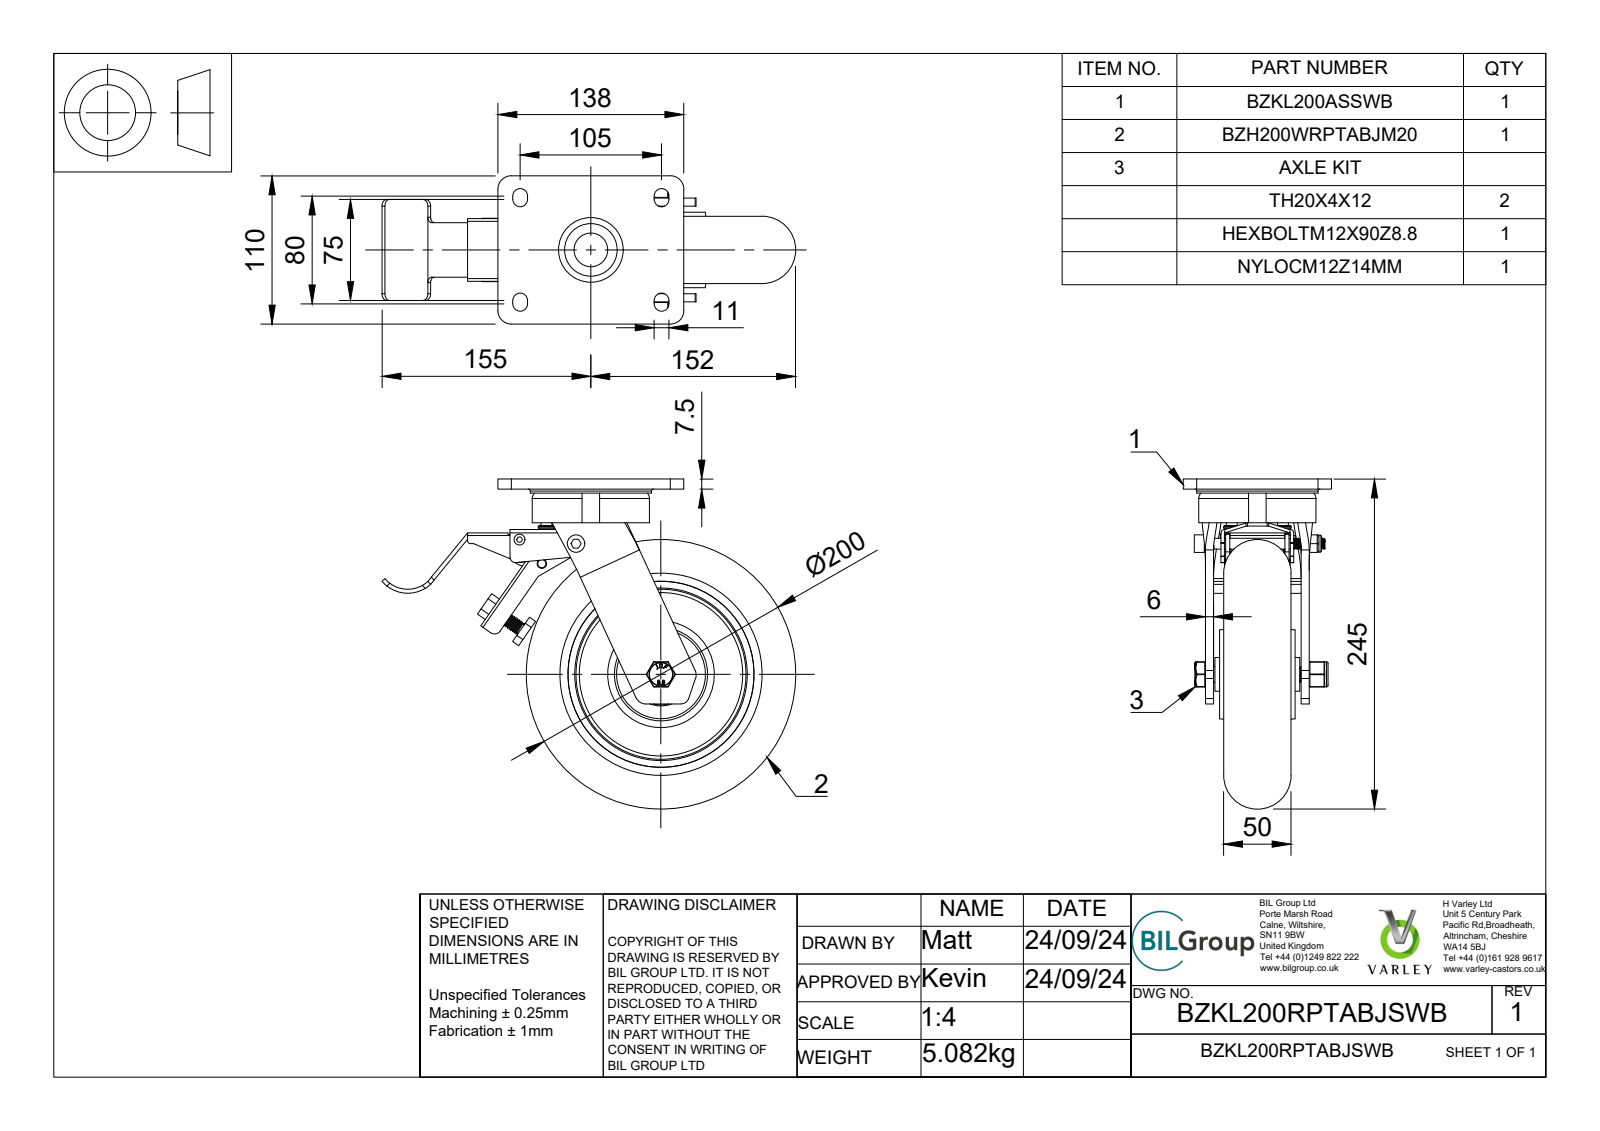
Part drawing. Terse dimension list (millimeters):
name: BZKL200RPTABJSWB v3; BZKL200ASSWB v1; FABRICATED STEEL TOP PLATE; FABRICATED STEEL FORKS (+8 more)
written by: Autodesk Translation Framework v13.20.0.188 (AUTOMOTIVE_DESIGN)
unit: mm
bodies: 50 solids, 1359 faces (570 planar, 359 cylindrical, 430 other)
size: 307 × 245 × 110
volume: 1 451 000 mm³; area: 370 843 mm²
holes: 12× ⌀9, 3× ⌀6, 1× ⌀8, 1× ⌀10, 1× ⌀12, 1× ⌀12.2, 1× ⌀13, 1× ⌀14, 1× ⌀20, 1× ⌀28.5, 1× ⌀30.8, 1× ⌀40.3
bosses: 12× ⌀9, 4× ⌀8, 2× ⌀12, 1× ⌀90, 1× ⌀88, 1× ⌀40.8, 1× ⌀31.3, 1× ⌀27
rounds: 18× R0.5, 8× R5.5, 6× R0.75, 6× R2, 6× R5, 4× R0.47, 4× R0.9, 4× R10
face distances: 7.5, 6, 35.5, 3.5, 9.5, 3, 31.5, 45, 29.5, 41.5
hole spacings: 76.5, 39.6, 108.19, 147.79, 132.5, 132.51, 153, 153.01
